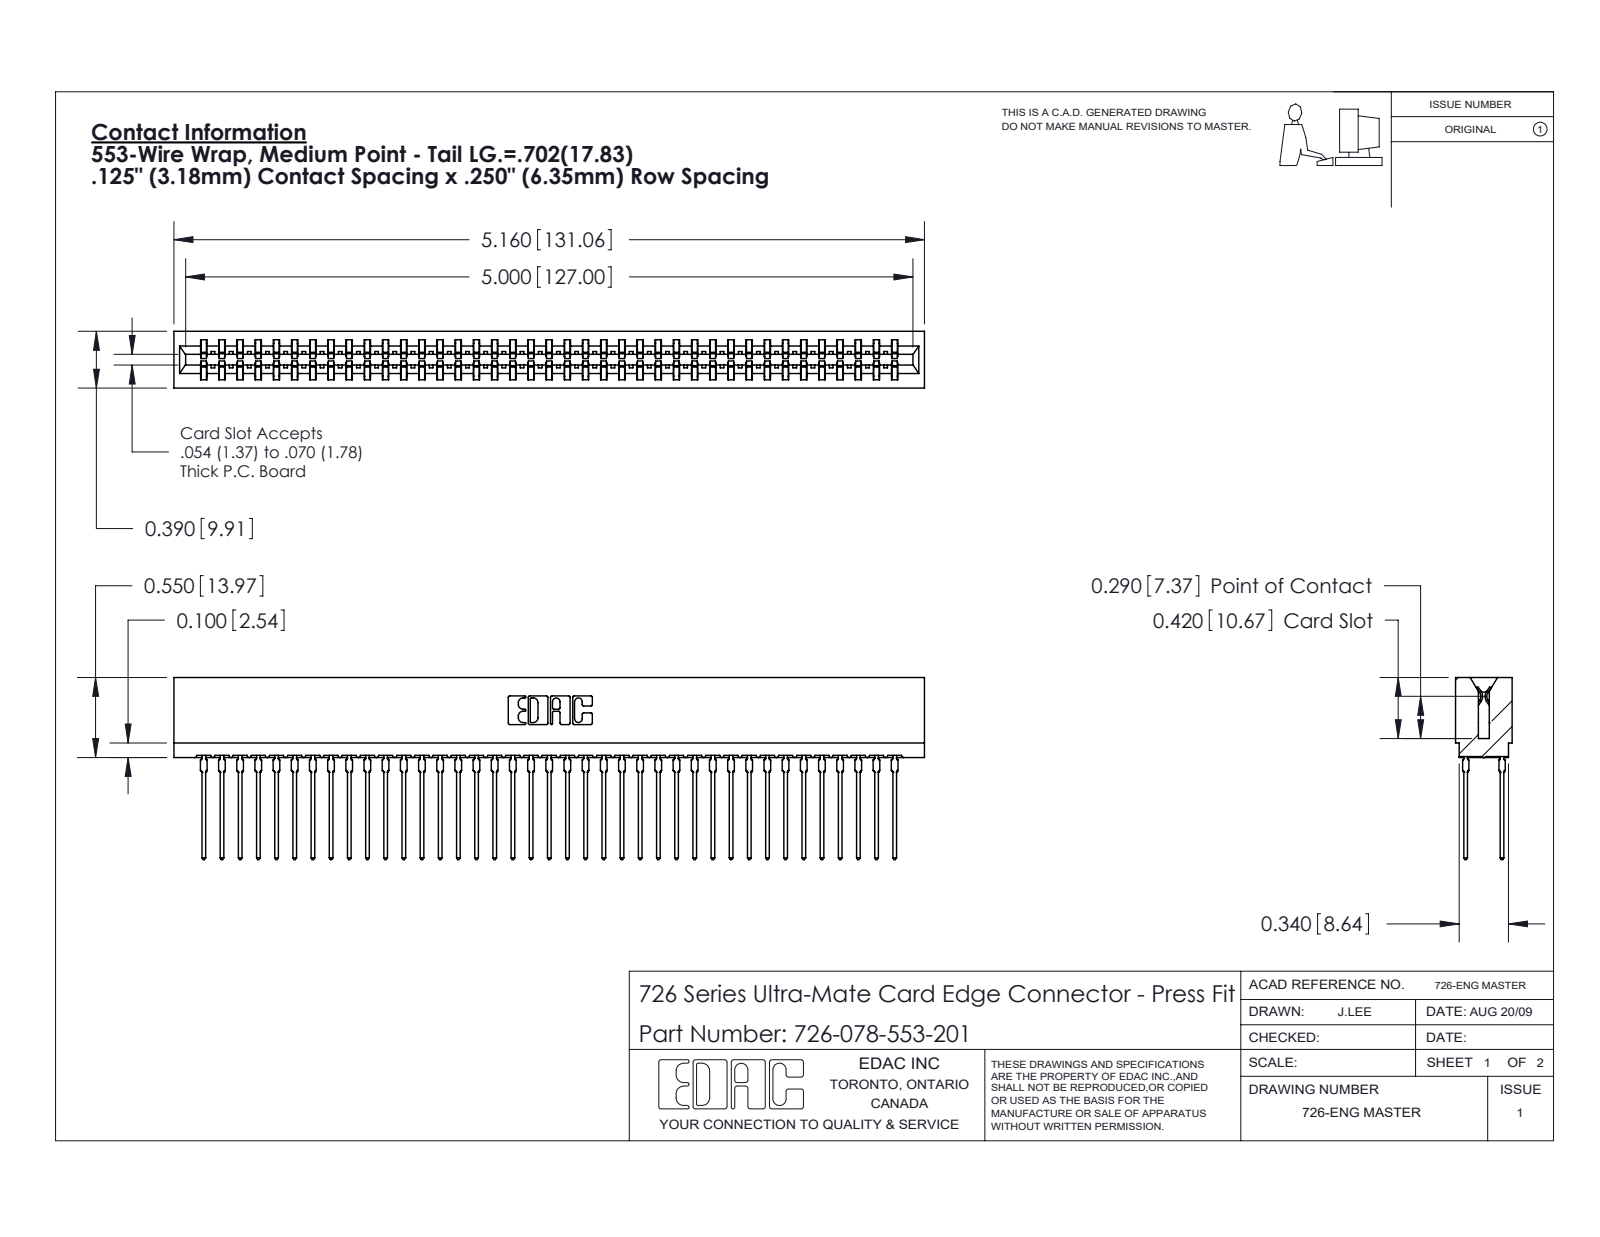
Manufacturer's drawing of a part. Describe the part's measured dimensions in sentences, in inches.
The part is named "726 Part_.515 Slot Depth - 01; 746-292-001_553; 726-078-553-201". Its 3-D file was written by "SolidWorks 2020 (CONFIG_CONTROL_DESIGN)". It is 79 solids with 7078 faces: 3643 planar, 1407 cylindrical and 2028 other. Overall it measures 5.16 by 1.251 by 0.39 inches. Its volume is 0.758 cubic inches and its surface area 34.46 square inches. Partial cylindrical surfaces (rounded edges, fillets, slot ends): 156 of radius 0.021, 40 of radius 0.015, 22 of radius 0.01, 8 of radius 0.005, 8 of radius 0.011, 6 of radius 0.007, 6 of radius 0.031, 3 of radius 0.026. The main face-to-face distances are 0.057, 0.333, 0.025, 0.307, 0.25, 0.083, 0.39, 0.275, 0.225, 0.365.
